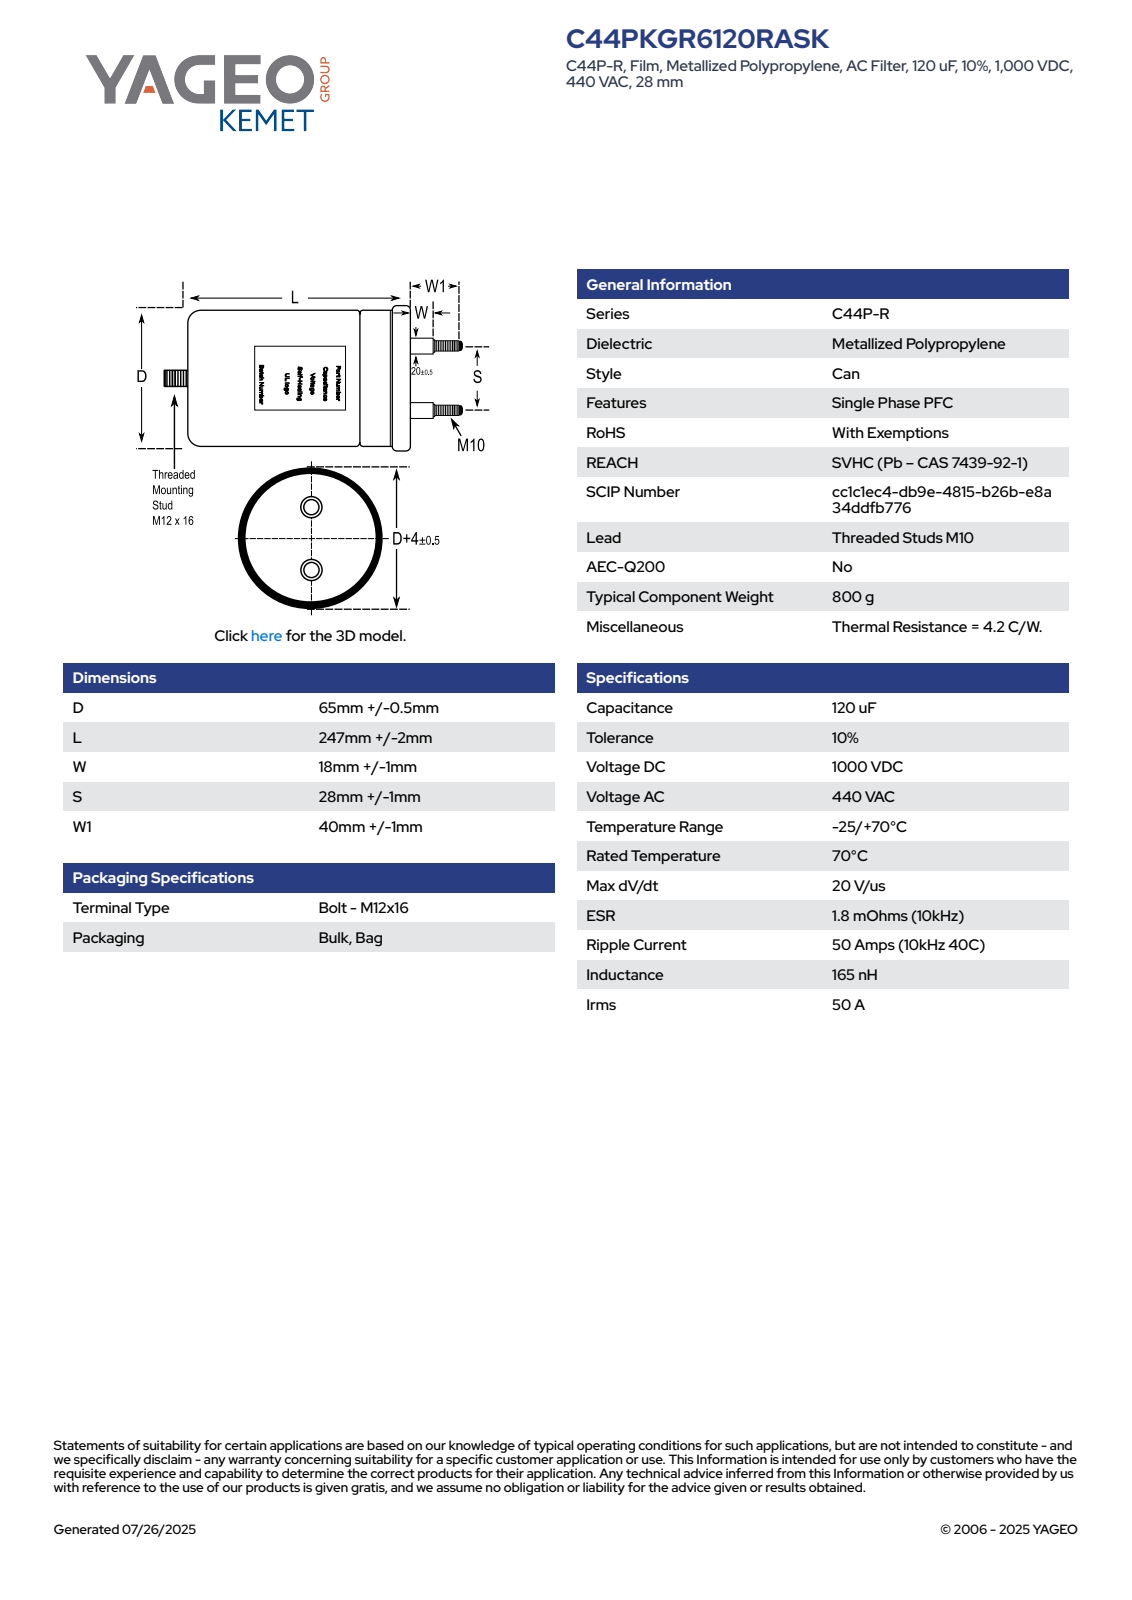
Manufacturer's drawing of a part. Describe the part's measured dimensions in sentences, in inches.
The part is named "CFP_C44P_65X197_D65.5L249S28". Its 3-D file was written by "SolidWorks 2014 (AUTOMOTIVE_DESIGN)". It is 1 solid with 105 faces: 32 planar, 36 cylindrical and 37 other. Overall it measures 12.047 by 2.756 by 2.756 inches. Its volume is 52.42 cubic inches and its surface area 97.32 square inches. Round bosses or shafts: 3 of diameter 0.472, 2 of diameter 0.807, 2 of diameter 0.394, 1 of diameter 2.756, 1 of diameter 2.579. Partial cylindrical surfaces (rounded edges, fillets, slot ends): 1 of radius 1.29. The main face-to-face distances are 9.803, 10.512, 0.709, 9.489, 0.315, 1.023, 11.417, 1.929, 1.614, 0.906.
